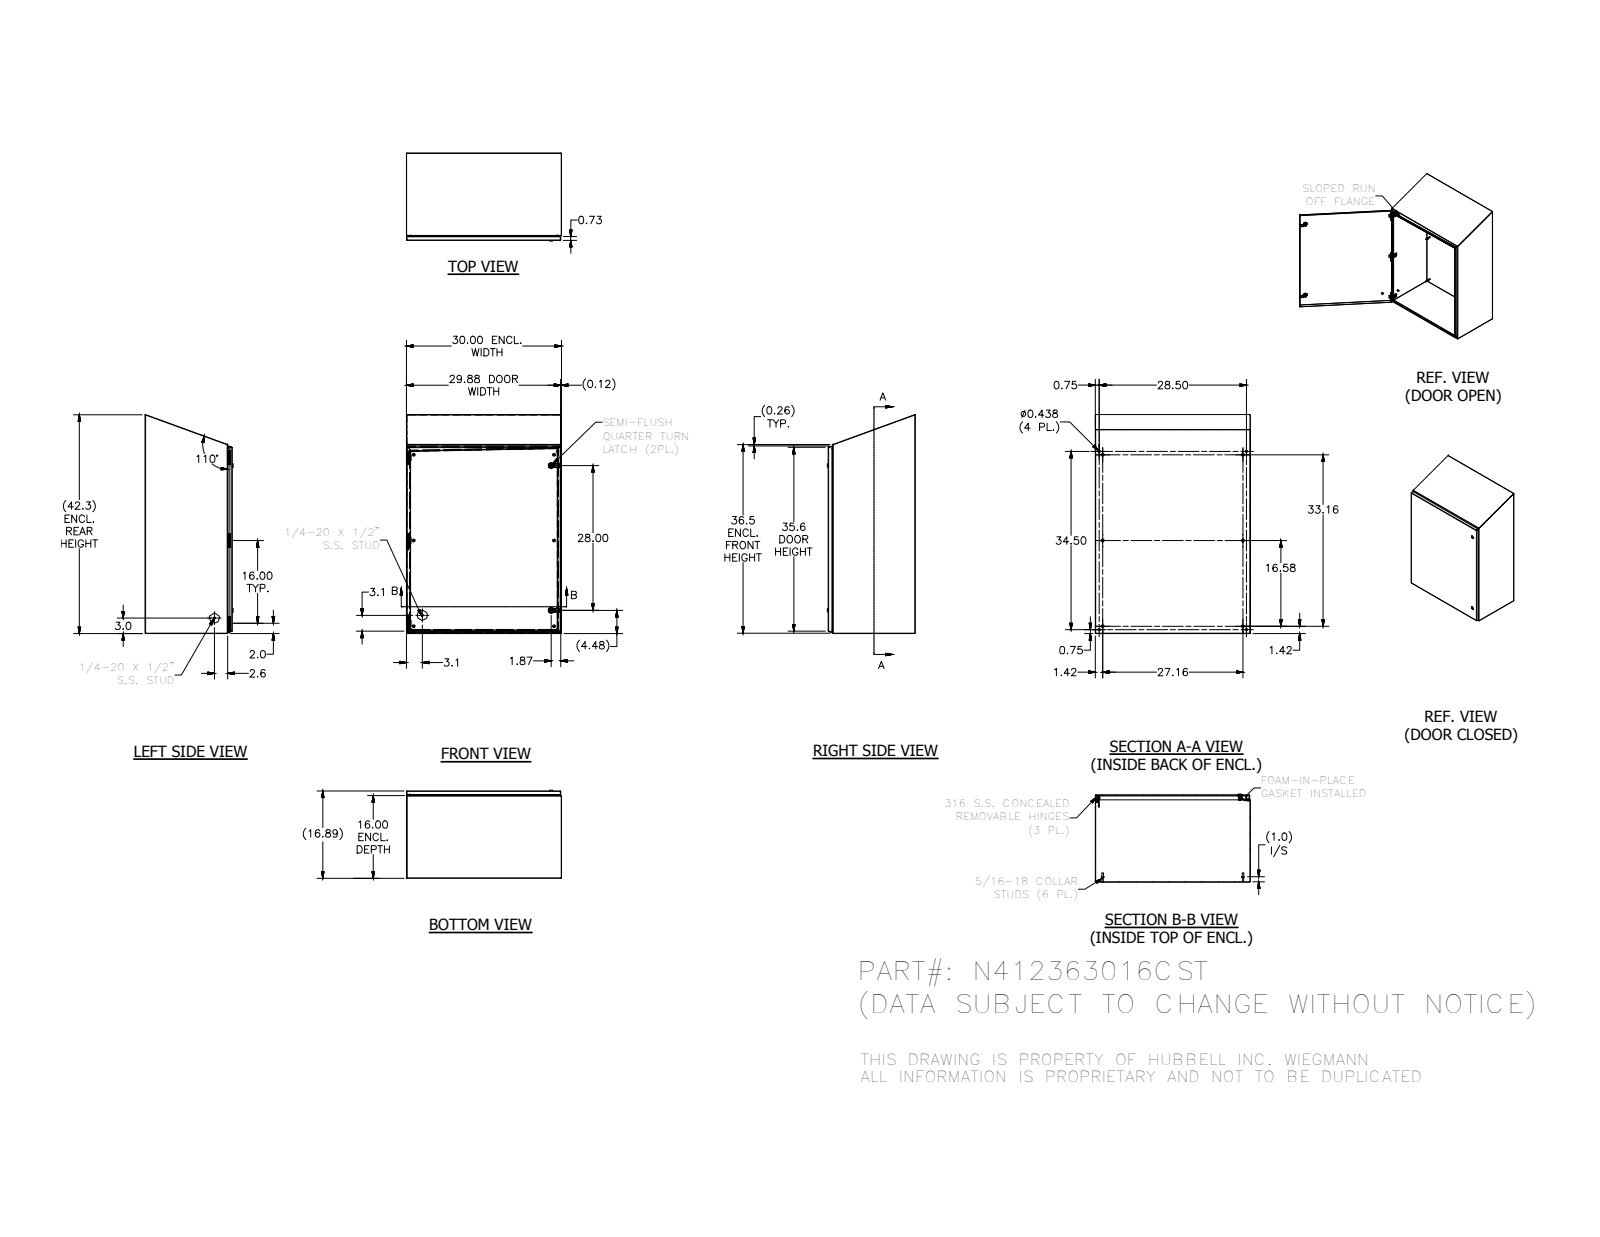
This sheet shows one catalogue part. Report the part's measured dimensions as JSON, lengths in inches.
{"part_name": "N412_CST-assm3pcblr; N412363016CSTBLR; HFW3161; HFW328176 (+8 more)", "step_written_by": "Autodesk Inventor 2012 (AUTOMOTIVE_DESIGN)", "units": "inches", "bodies": {"solids": 52, "faces": 2350, "planar": 904, "cylindrical": 864, "other": 582}, "overall_size": [42.377, 30, 17.044], "volume_in3": 360.8, "surface_area_in2": 9822, "round_holes": [[0.093, 6], [0.152, 6], [0.167, 6], [0.172, 6], [0.187, 6], [0.156, 4], [0.437, 4], [0.197, 2], [0.315, 2], [0.394, 2], [0.402, 2], [0.634, 2]], "round_bosses_or_shafts": [[0.25, 14], [0.563, 6], [0.36, 6], [0.32, 6], [0.3, 6], [0.275, 6], [0.256, 6], [0.164, 6]], "partial_cylinders_radius": [[0.012, 54], [0.05, 38], [0.031, 32], [0.016, 26], [0.125, 24], [0.02, 23], [0.105, 18], [0.032, 12]], "face_to_face_distances": [0.074, 16.813, 29.926, 16.739, 16.887, 29.852, 30, 15.926, 0.887, 0.813], "hole_center_spacings": [16, 32, 16.008, 0.5, 0.656, 0.66, 1.307, 1.311]}
